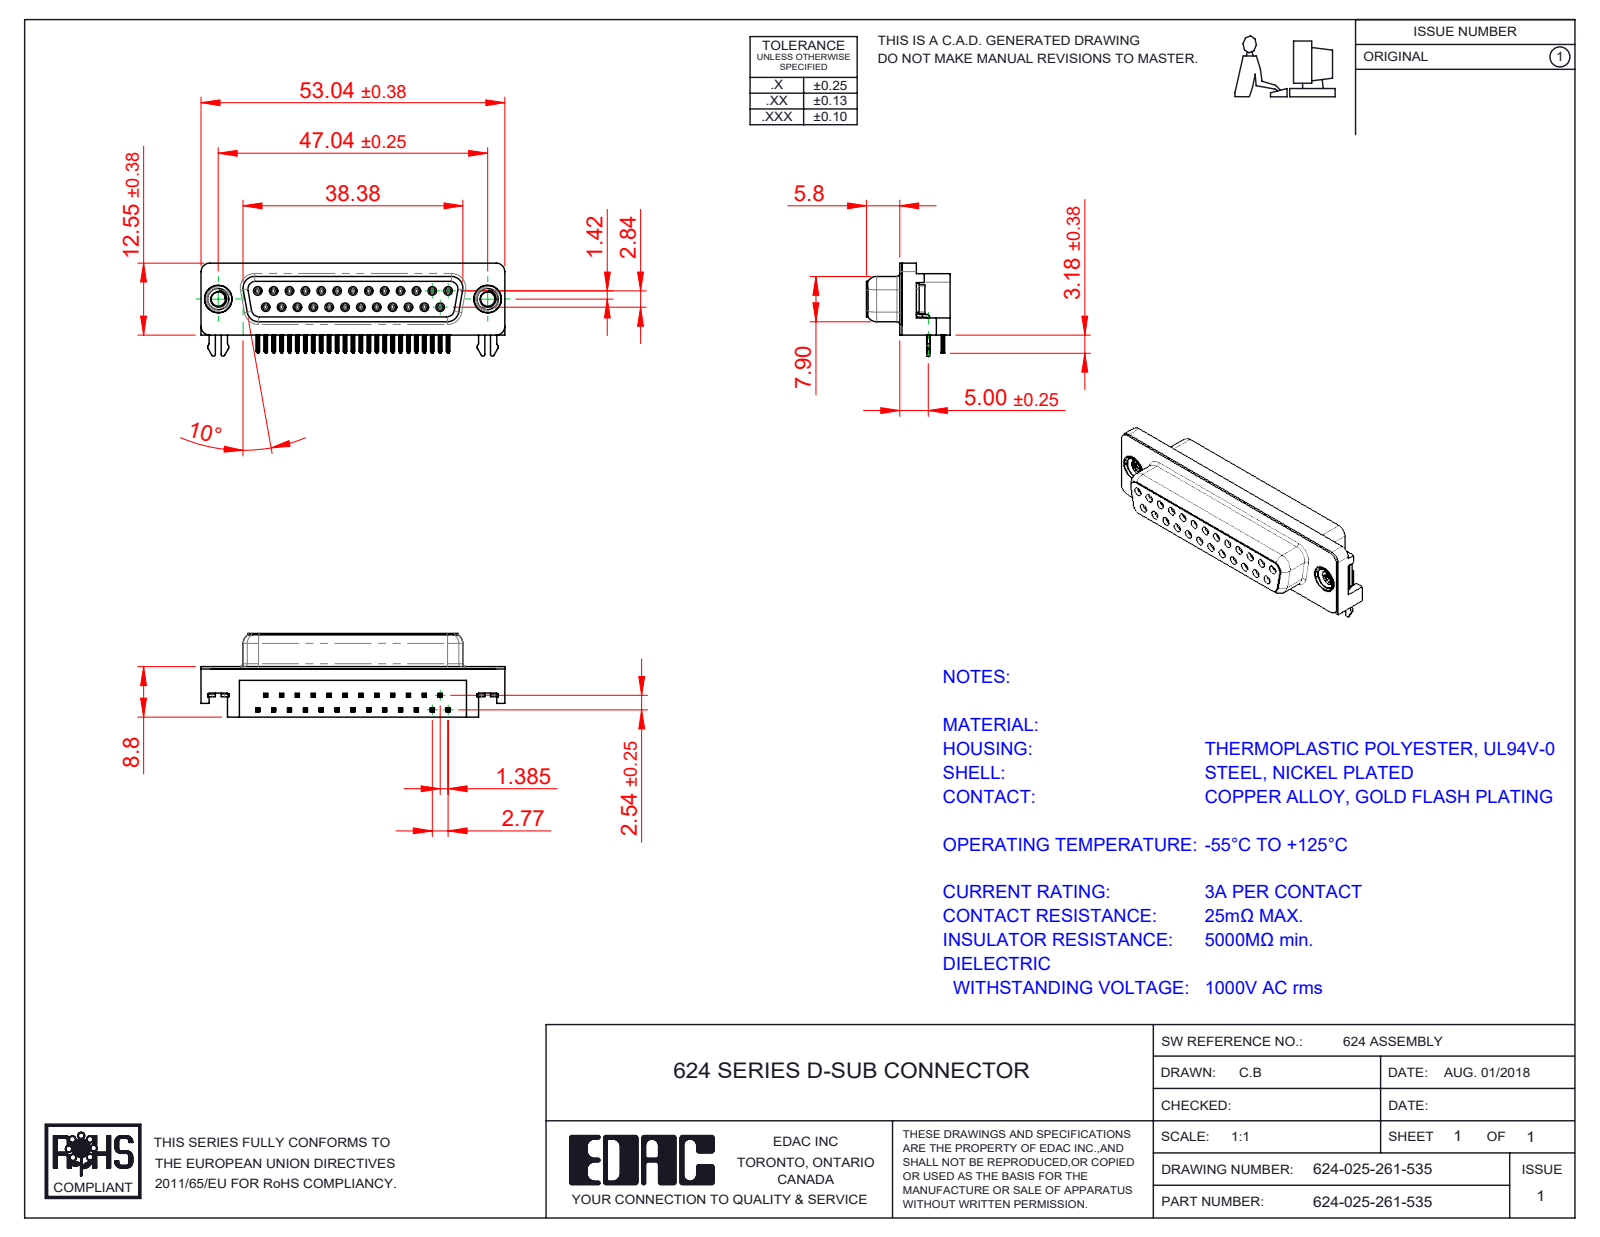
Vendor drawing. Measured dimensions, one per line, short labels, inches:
name: 624 2 Prong Board Lock; 624 M3 Threaded Rivet; 624-025-261-535; 624 Contact Top (+3 more)
written by: SolidWorks 2016 (CONFIG_CONTROL_DESIGN)
unit: in
bodies: 31 solids, 3752 faces (1630 planar, 918 cylindrical, 1204 other)
size: 2.088 × 0.64 × 0.575
volume: 0.363 in³; area: 12.83 in²
holes: 25× ⌀0.031, 25× ⌀0.035, 2× ⌀0.098, 2× ⌀0.157, 2× ⌀0.189, 2× ⌀0.197
bosses: 25× ⌀0.047, 2× ⌀0.193, 2× ⌀0.187, 2× ⌀0.154
rounds: 200× R0.004, 100× R0.006, 50× R0.014, 25× R0.013, 12× R0.011, 10× R0.02, 10× R0.039, 8× R0.01
face distances: 0.016, 0.244, 0.331, 0.125, 0.369, 0.346, 0.107, 0.114, 0.033, 0.278
hole spacings: 0.124, 0.109, 0.218, 0.327, 0.436, 0.198, 0.198, 0.294
